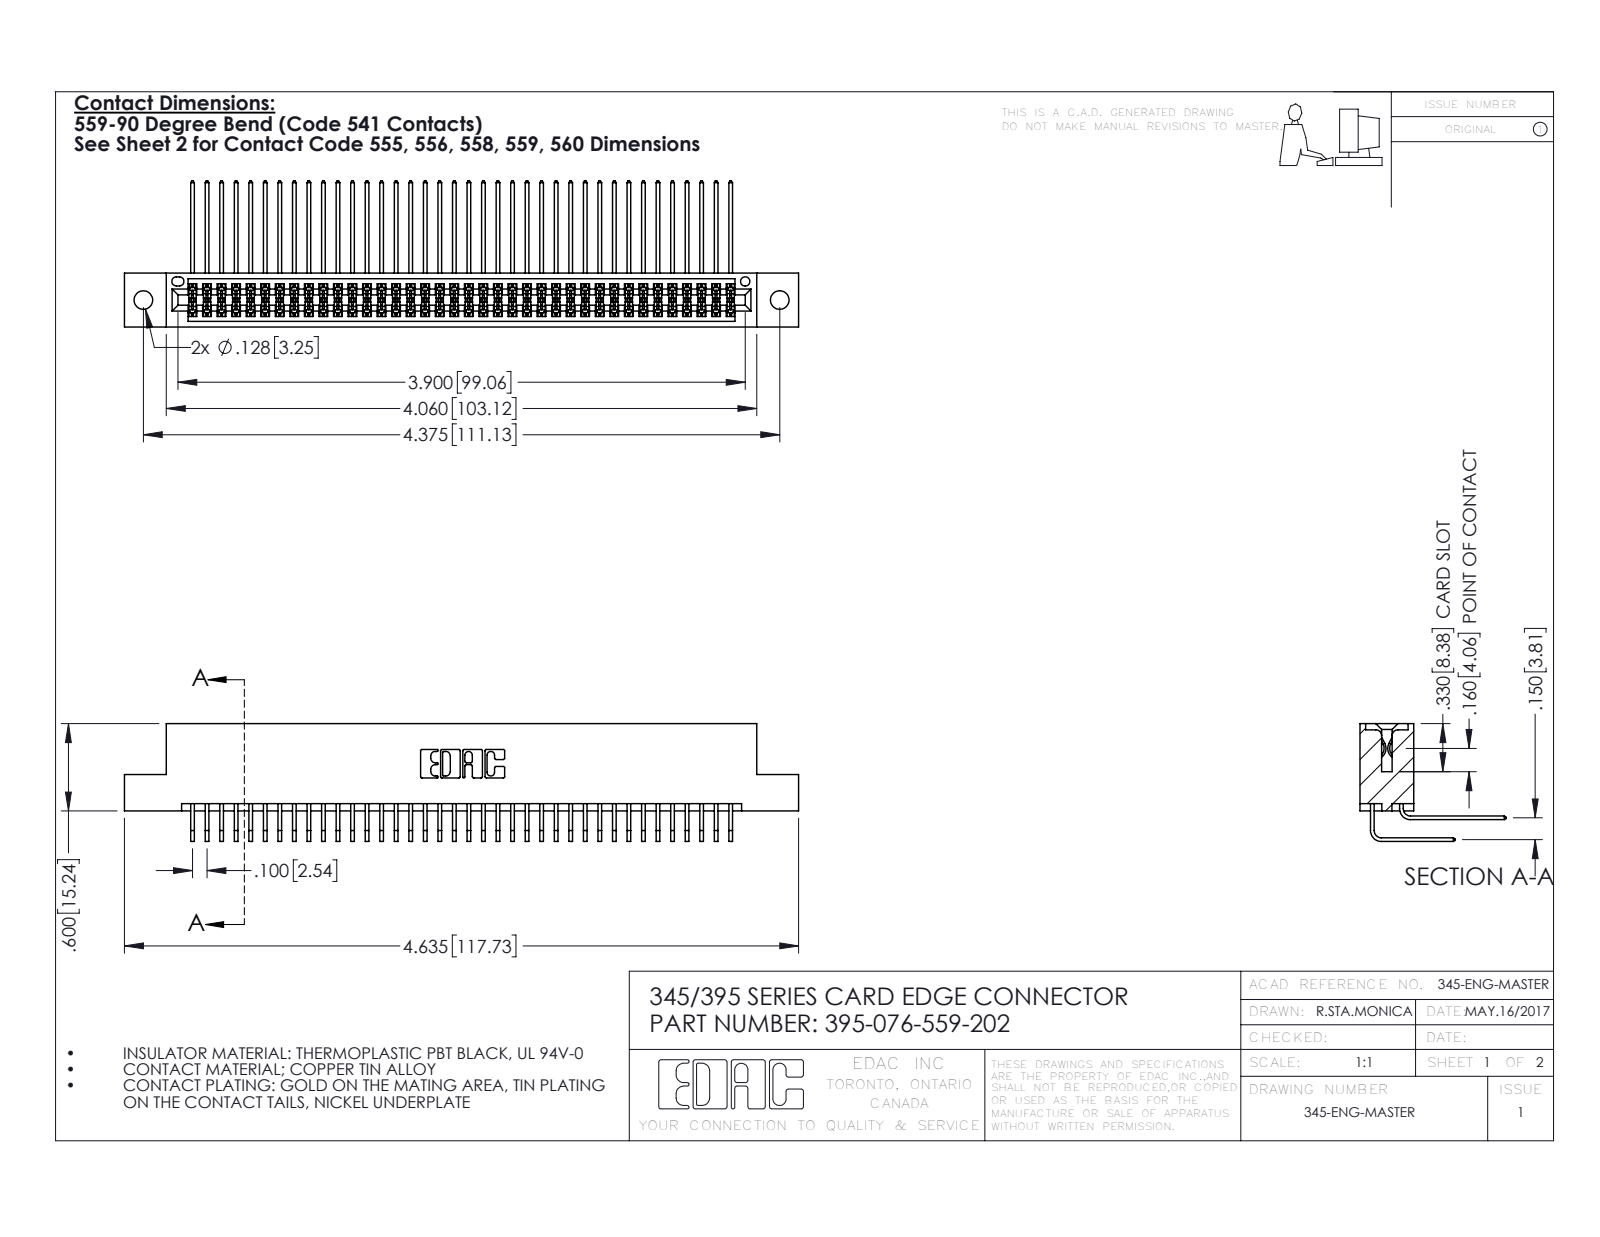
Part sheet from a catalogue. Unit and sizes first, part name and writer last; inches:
Units: inches
Overall size (bounding box): 4.635 × 1.005 × 0.809
Round holes (diameter × count): ⌀0.128 ×2, ⌀0.064 ×1
Partial cylindrical surfaces — rounded edges, fillets, slot ends (radius × count): R0.006 ×114, R0.01 ×22, R0.007 ×6, R0.031 ×6, R0.026 ×3, R0.014 ×2, R0.019 ×2, R0.022 ×2
Main face-to-face distances: 0.072, 0.298, 0.2, 0.37, 0.098, 0.272, 0.025, 0.225, 0.175, 0.15
Hole centre spacings: 0.27, 4.139, 4.375
Volume: 0.72 in³ · Surface area: 29.69 in²
Bodies: 77 solids, 4078 faces (2740 planar, 1338 cylindrical, 0 other)
Part name (STEP PRODUCT): 395-076-559-202; 345-292-001_559 Tail - 2; 345-292-001_558 559 Tail - 1; 345 Part_Flush Mounting Lugs - 0.128 Dia
STEP written by: SolidWorks 2016 (CONFIG_CONTROL_DESIGN)
